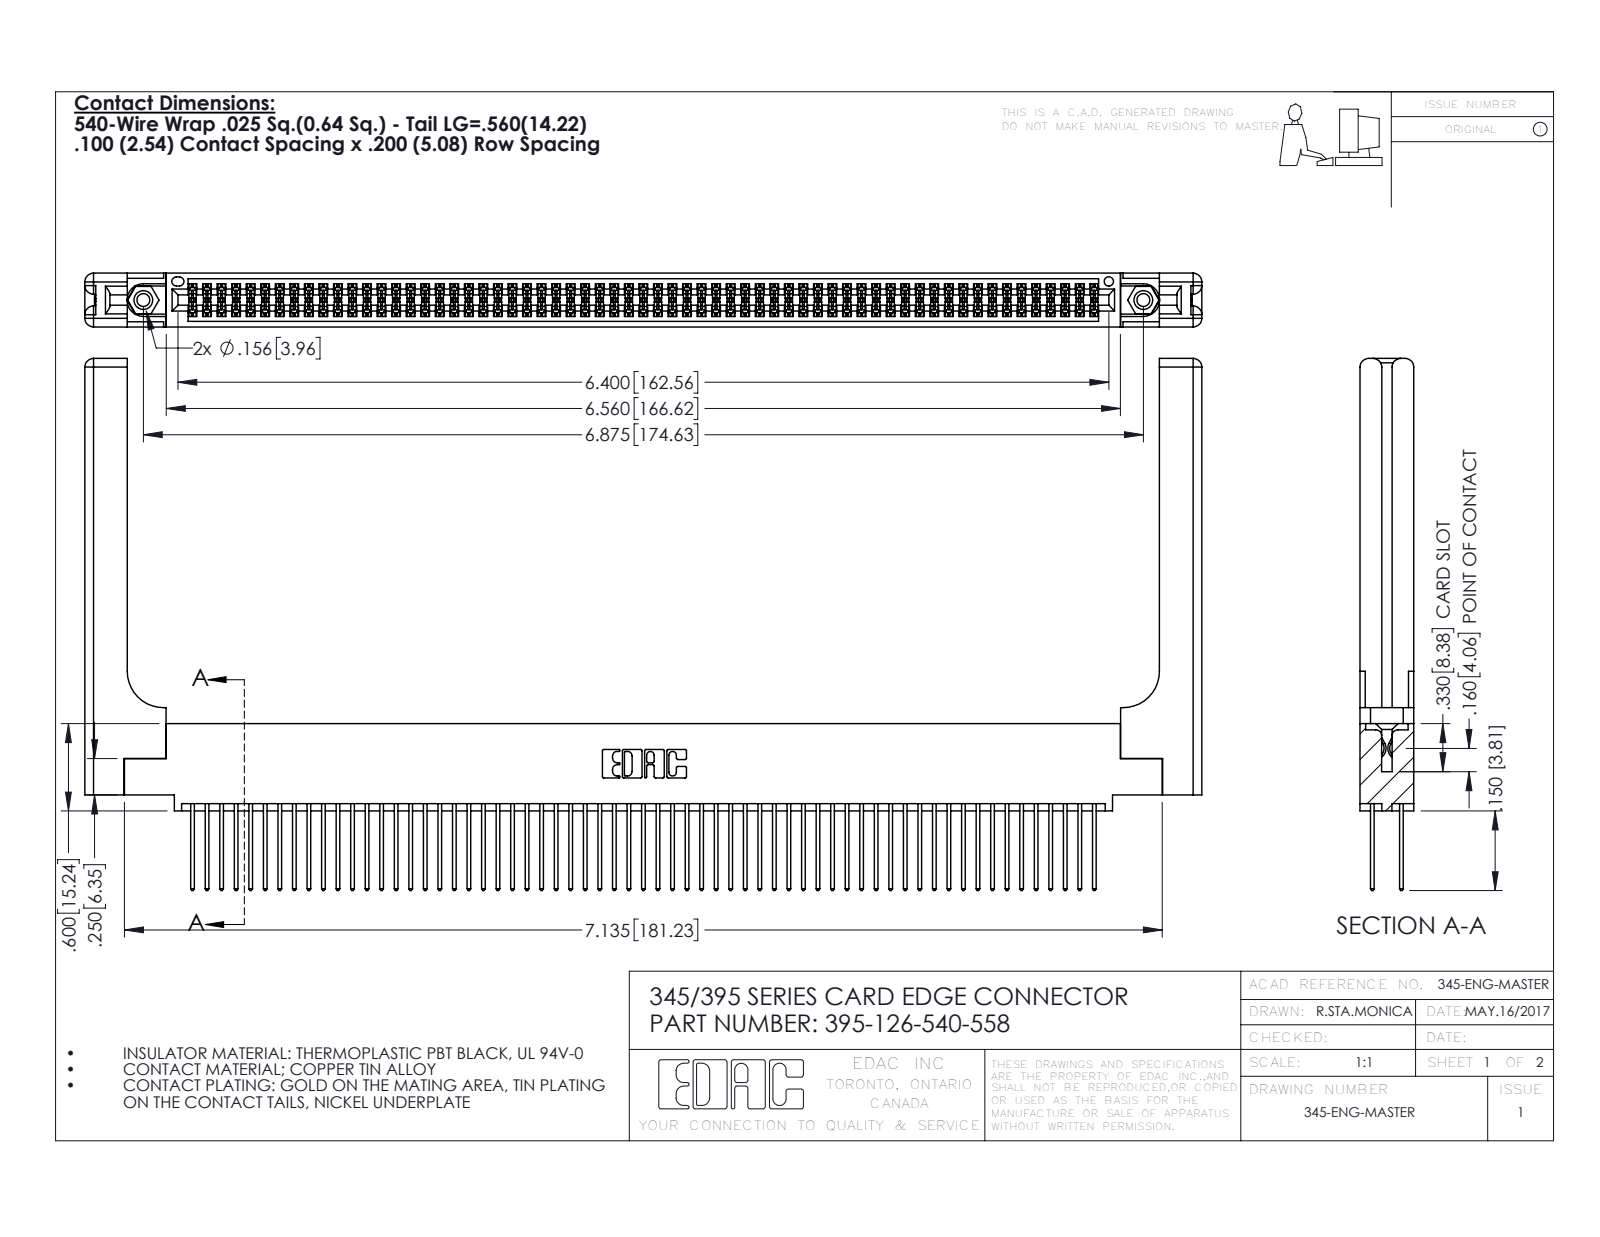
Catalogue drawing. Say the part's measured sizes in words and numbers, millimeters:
The part is named "345-220-058_345-220-058; 345-292-001_345-293-140; 395-126-540-558; 345 Part_0.110 Offset - 0.156 Dia-TH (+1 more)". Its 3-D file was written by "SolidWorks 2016 (CONFIG_CONTROL_DESIGN)". It is 131 solids with 6686 faces: 4390 planar, 2236 cylindrical and 60 other. Overall it measures 195 by 92.9 by 9.4 millimeters. Its volume is 28 020 cubic millimeters and its surface area 36 660 square millimeters. Round holes: 2 of diameter 2.3, 2 of diameter 3.2, 2 of diameter 4, 1 of diameter 1.6. Round bosses or shafts: 2 of diameter 3.9. Partial cylindrical surfaces (rounded edges, fillets, slot ends): 189 of radius 0.2, 126 of radius 0.3, 22 of radius 0.3, 16 of radius 1.5, 6 of radius 0.2, 6 of radius 0.8, 3 of radius 0.7, 2 of radius 0.4. The main face-to-face distances are 1.8, 7.6, 9.4, 2.5, 6.9, 0.6, 5.1, 5.7, 4.4, 3.8. The hole center spacings are 6.9, 168.6, 174.6.
